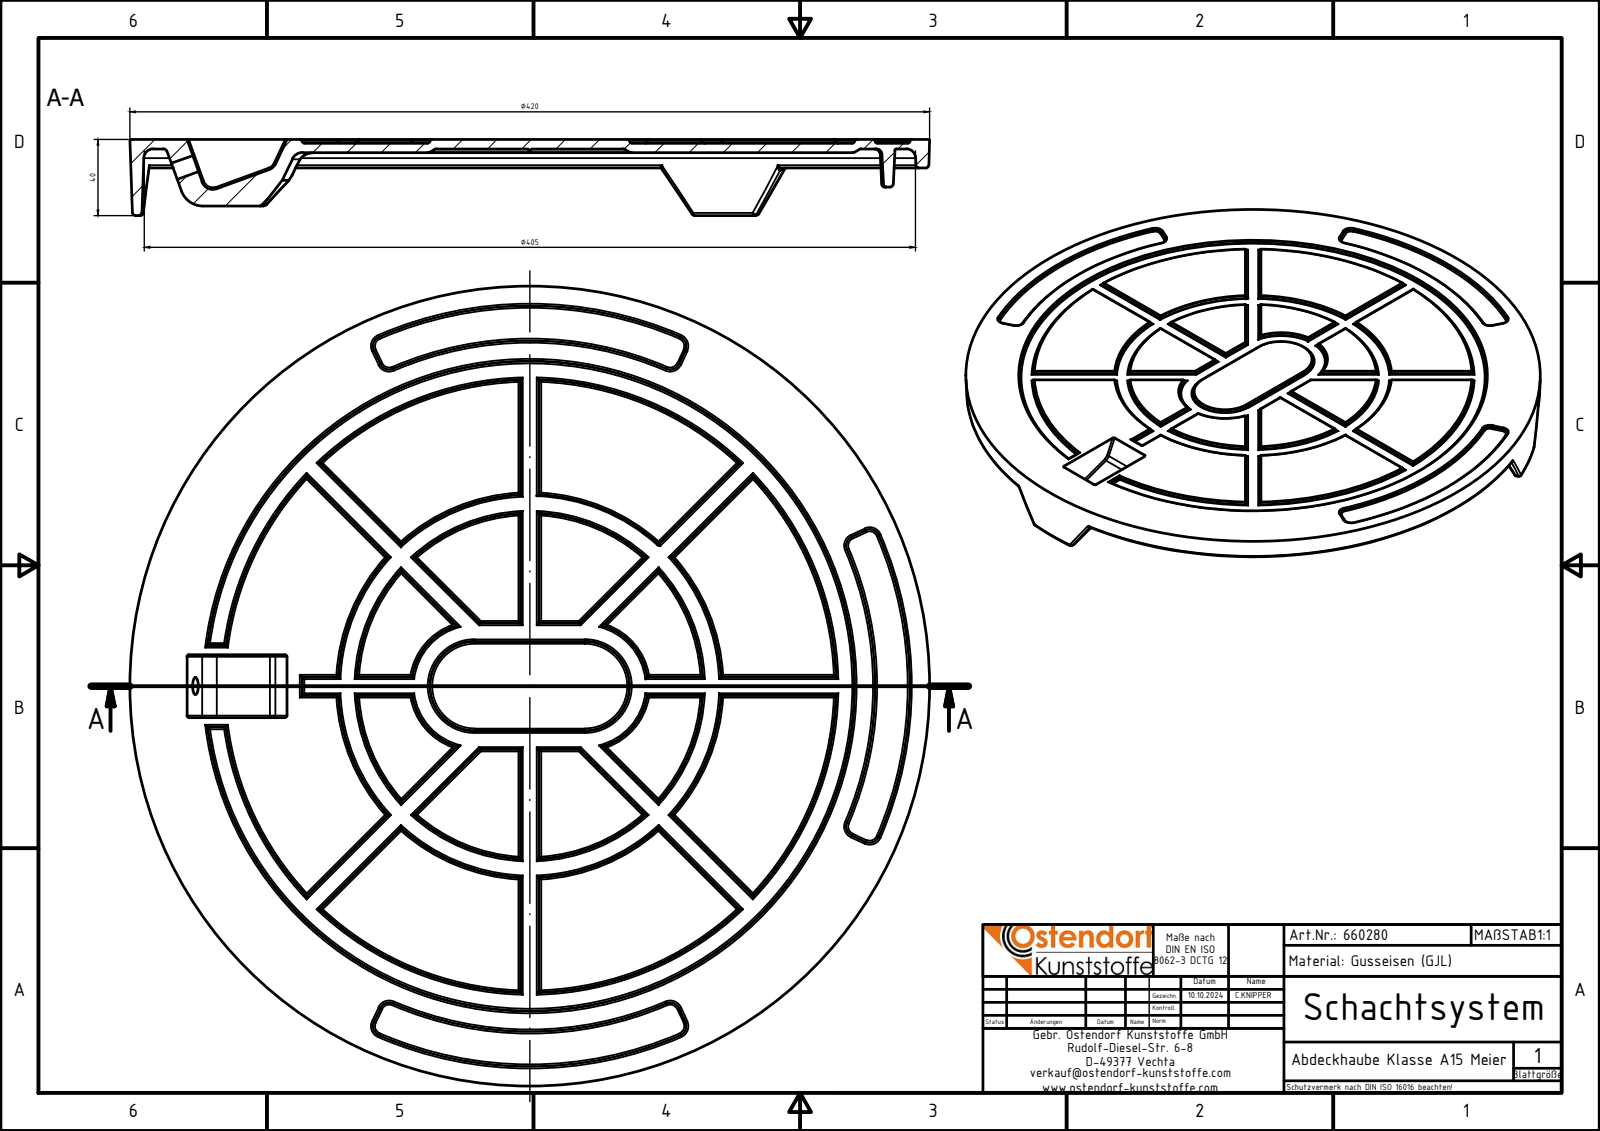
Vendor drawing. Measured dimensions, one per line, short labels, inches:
name: 660280z
written by: Autodesk Inventor 2024 (AUTOMOTIVE_DESIGN)
unit: in
bodies: 1 solid, 744 faces (98 planar, 135 cylindrical, 511 other)
size: 16.535 × 16.535 × 1.575
volume: 60.01 in³; area: 508.1 in²
holes: 1× ⌀0.354
rounds: 66× R0.039, 10× R0.059, 4× R0.079, 3× R0.236, 2× R0.024, 1× R0.197
face distances: 0.276, 0.197, 0.079, 0.118, 0.394, 0.591, 0.315, 0.512, 1.299, 1.378
